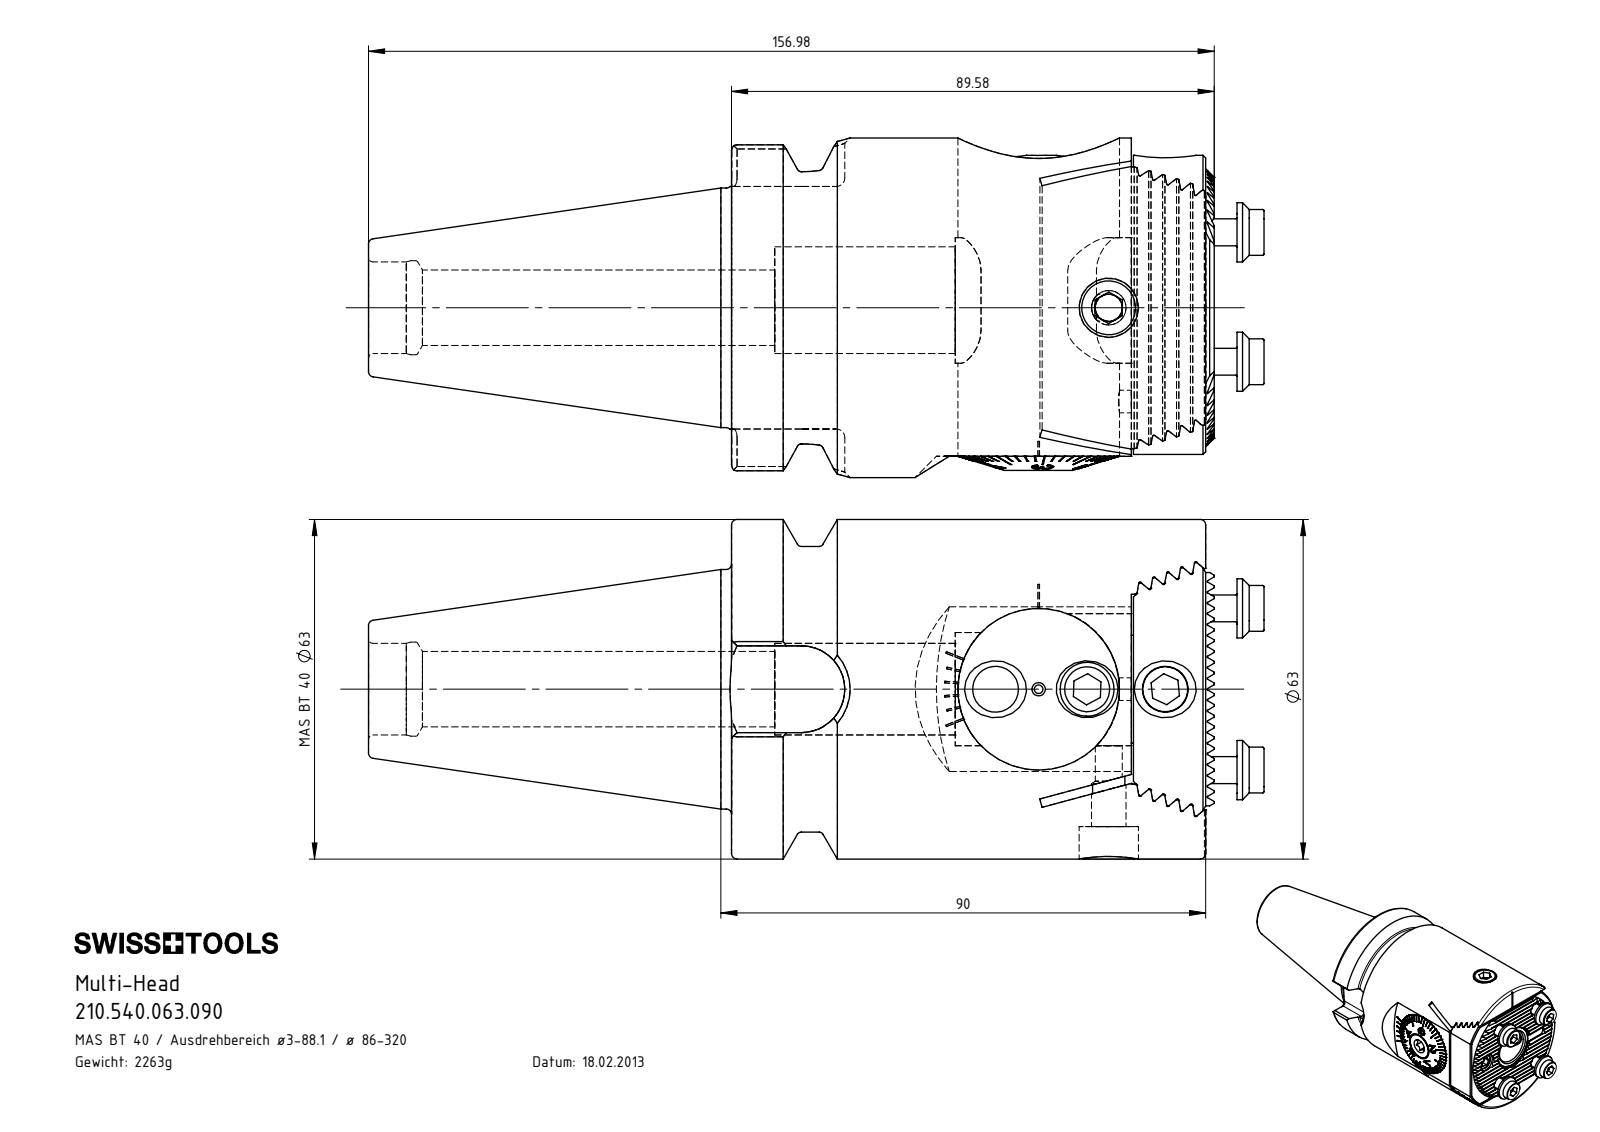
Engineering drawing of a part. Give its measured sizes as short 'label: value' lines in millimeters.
name: MH1-BG1.001.049_B; A55-BG2.015.007_A; A55-BG2.014.007_A; BT4-MH1.K00.090_A (+8 more)
written by: SolidWorks 2015 (CONFIG_CONTROL_DESIGN)
unit: mm
bodies: 18 solids, 1198 faces (601 planar, 266 cylindrical, 331 other)
size: 168.98 × 63 × 63
volume: 288 156 mm³; area: 75 895 mm²
holes: 5× ⌀4.2, 4× ⌀8.5, 3× ⌀6.8, 3× ⌀11, 2× ⌀14, 2× ⌀20, 1× ⌀1, 1× ⌀1.6, 1× ⌀3.3, 1× ⌀5, 1× ⌀6.4, 1× ⌀8
bosses: 4× ⌀11, 4× ⌀8.5, 4× ⌀5, 3× ⌀10, 1× ⌀63, 1× ⌀53, 1× ⌀44.45, 1× ⌀30
rounds: 21× R0.14, 20× R0.2, 8× R1.6, 6× R6, 2× R4, 2× R31, 1× R2, 1× R7
face distances: 2.38, 0.4, 1.73, 4.77, 4.76, 8.66, 74.2, 74.6, 7.15, 5.2
hole spacings: 16.73, 18.03, 20.52, 24, 30, 34.8, 38.42, 7.28
